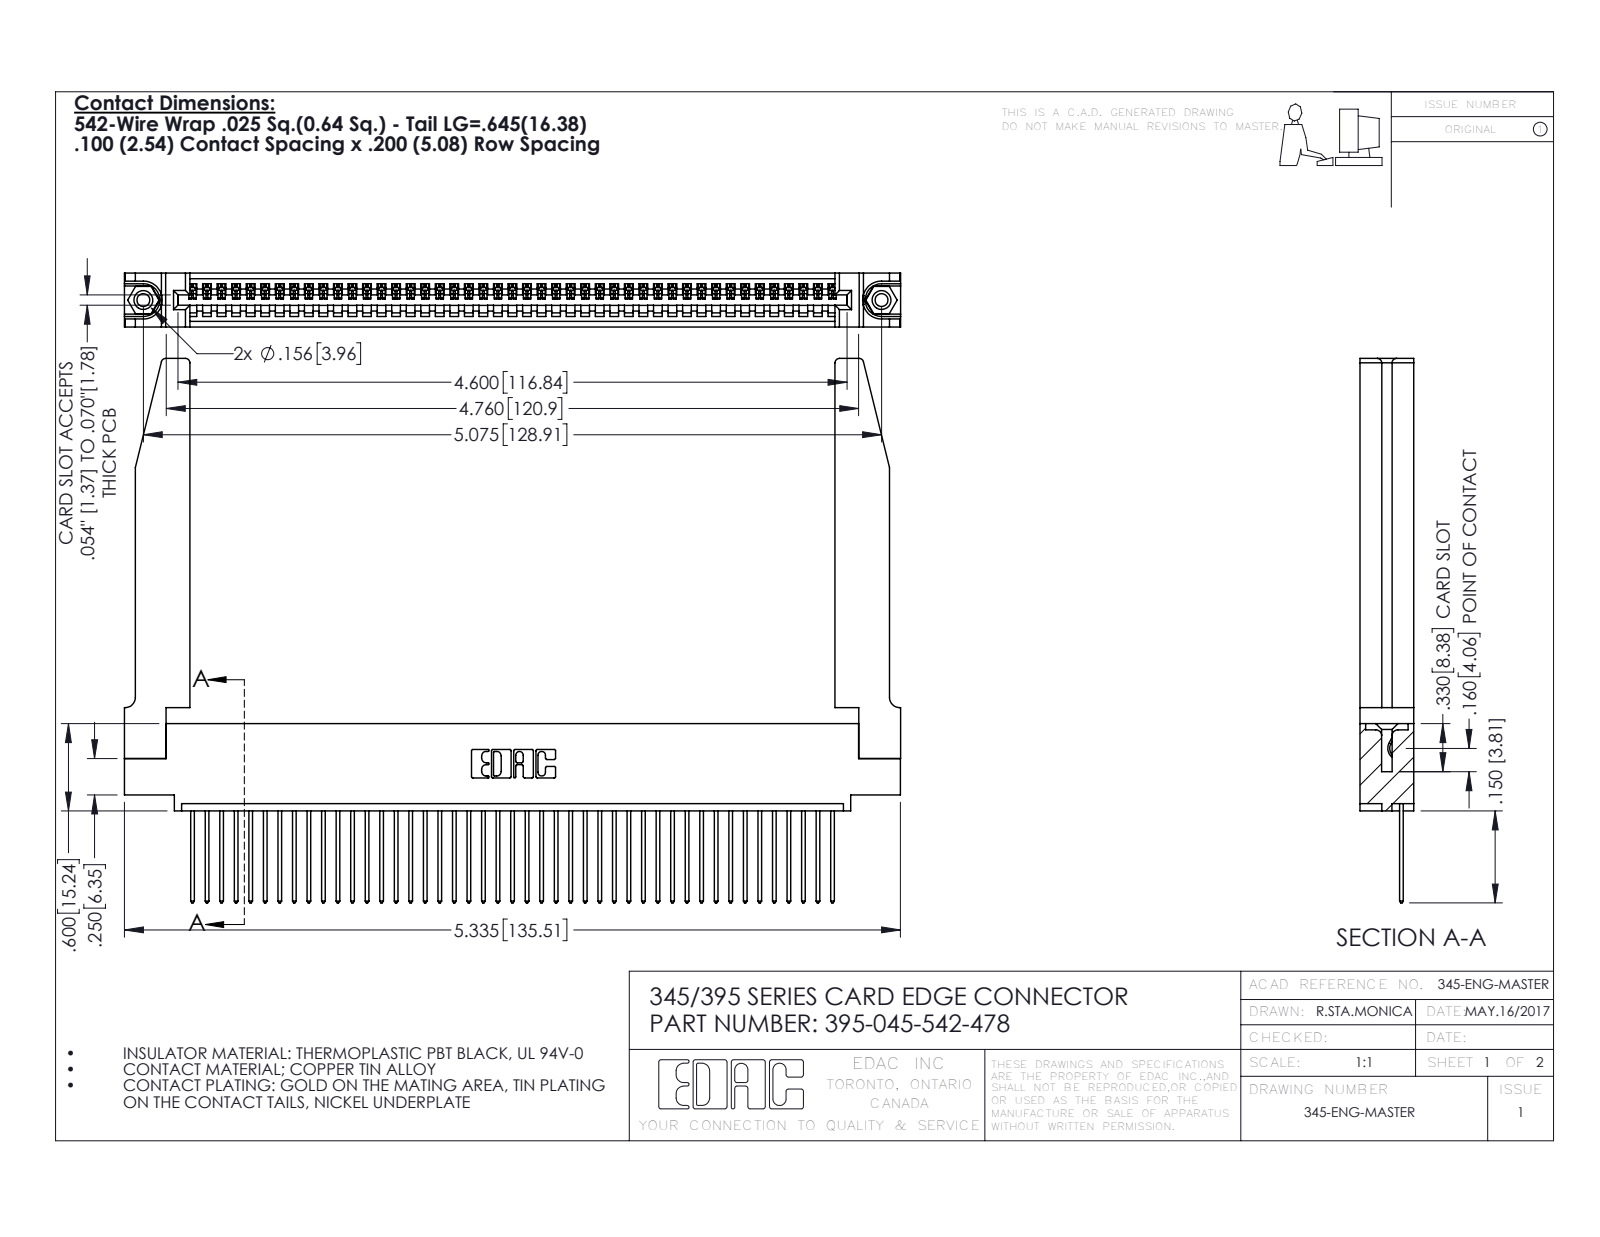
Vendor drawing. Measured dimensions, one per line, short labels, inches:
name: 345-220-078_345-220-078; 345-292-001_345-293-142; 395-045-542-478; 345-250-001_345-250-001-102 (+1 more)
written by: SolidWorks 2016 (CONFIG_CONTROL_DESIGN)
unit: in
bodies: 50 solids, 2974 faces (2026 planar, 896 cylindrical, 52 other)
size: 5.336 × 3.742 × 0.37
volume: 1.263 in³; area: 38.4 in²
holes: 2× ⌀0.089, 2× ⌀0.125, 2× ⌀0.156, 1× ⌀0.064
bosses: 2× ⌀0.155
rounds: 90× R0.006, 90× R0.01, 22× R0.01, 8× R0.03, 6× R0.007, 6× R0.031, 3× R0.026, 2× R0.031
face distances: 0.072, 0.37, 0.298, 0.098, 0.272, 0.025, 0.2, 0.225, 0.148, 0.15
hole spacings: 0.27, 4.839, 5.075
